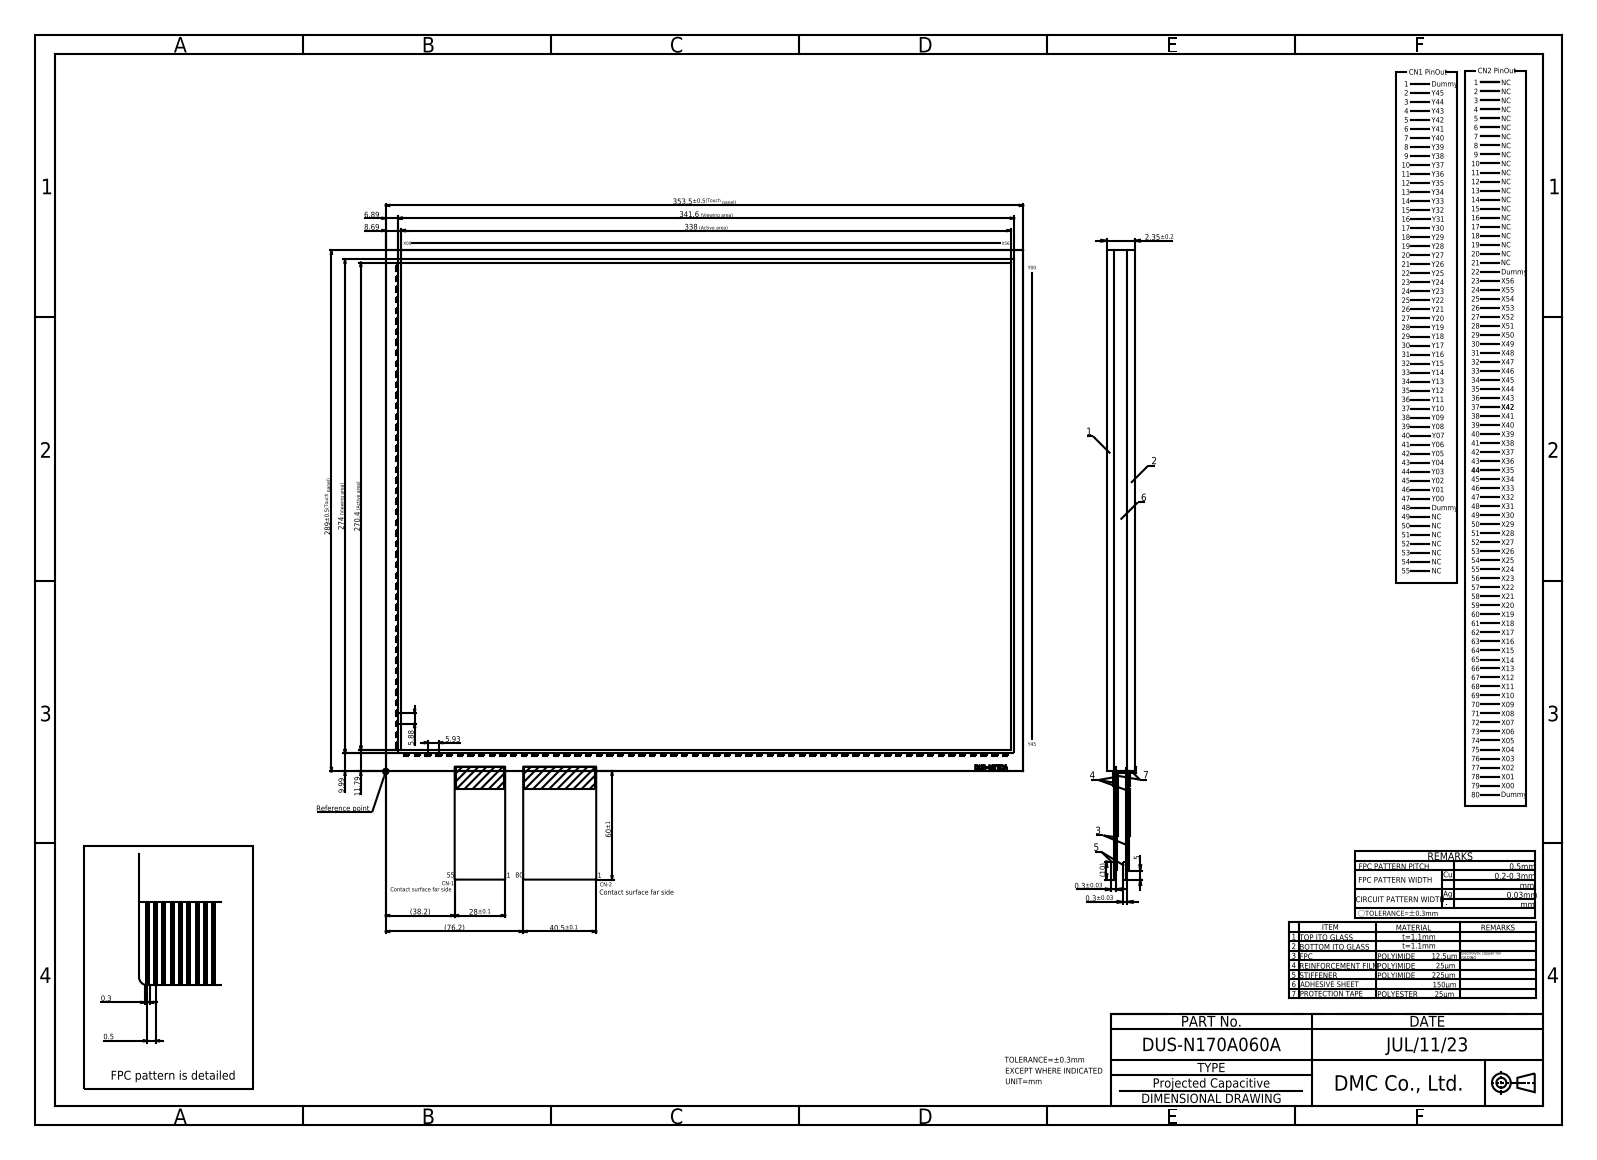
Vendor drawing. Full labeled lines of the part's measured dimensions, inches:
Part name (STEP PRODUCT): DUS-N170A060A
STEP written by: Autodesk Inventor 2020 (CONFIG_CONTROL_DESIGN)
Units: inches
Bodies: 1 solid, 578 faces (574 planar, 4 cylindrical, 0 other)
Overall size (bounding box): 19.484 × 16.016 × 0.093
Volume: 14.67 in³ · Surface area: 334.6 in²
Partial cylindrical surfaces — rounded edges, fillets, slot ends (radius × count): R0.008 ×4
Main face-to-face distances: 0.093, 0.043, 0.047, 0.045, 0.049, 0.039, 0.089, 11.378, 0.031, 0.028
